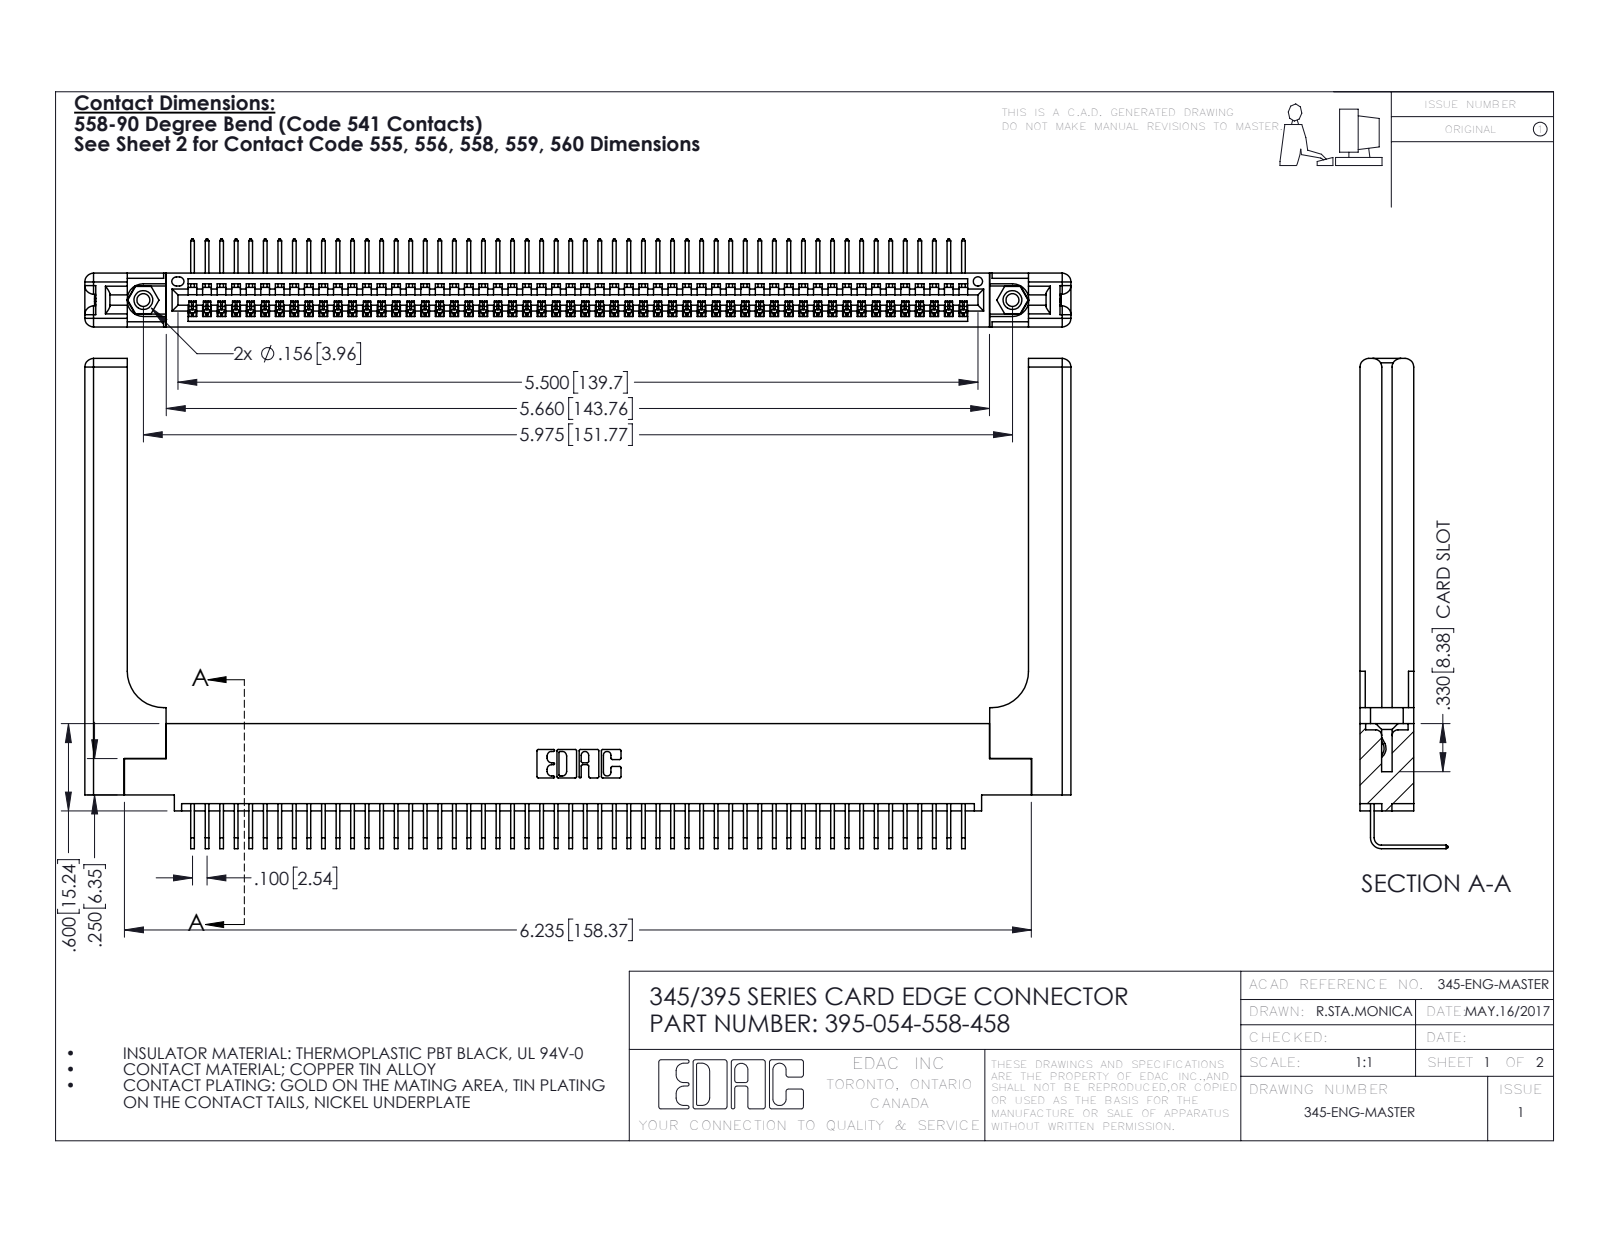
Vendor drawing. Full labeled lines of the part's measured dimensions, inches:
Part name (STEP PRODUCT): 345-250-001_345-250-001-102; 395-054-558-458; 345 Part_0.110 Offset - 0.156 Dia-TH; 345-220-058_345-220-058 (+1 more)
STEP written by: SolidWorks 2016 (CONFIG_CONTROL_DESIGN)
Units: inches
Bodies: 59 solids, 3626 faces (2500 planar, 1066 cylindrical, 60 other)
Overall size (bounding box): 6.779 × 3.369 × 0.605
Volume: 1.53 in³ · Surface area: 44.35 in²
Round holes (diameter × count): ⌀0.089 ×2, ⌀0.125 ×2, ⌀0.156 ×2, ⌀0.064 ×1
Round bosses / shafts (diameter × count): ⌀0.155 ×2
Partial cylindrical surfaces — rounded edges, fillets, slot ends (radius × count): R0.006 ×108, R0.01 ×22, R0.06 ×16, R0.007 ×6, R0.031 ×6, R0.026 ×3, R0.03 ×2, R0.031 ×2
Main face-to-face distances: 0.072, 0.37, 0.298, 0.098, 0.272, 0.025, 0.2, 0.225, 0.148, 0.15
Hole centre spacings: 0.27, 5.739, 5.975
